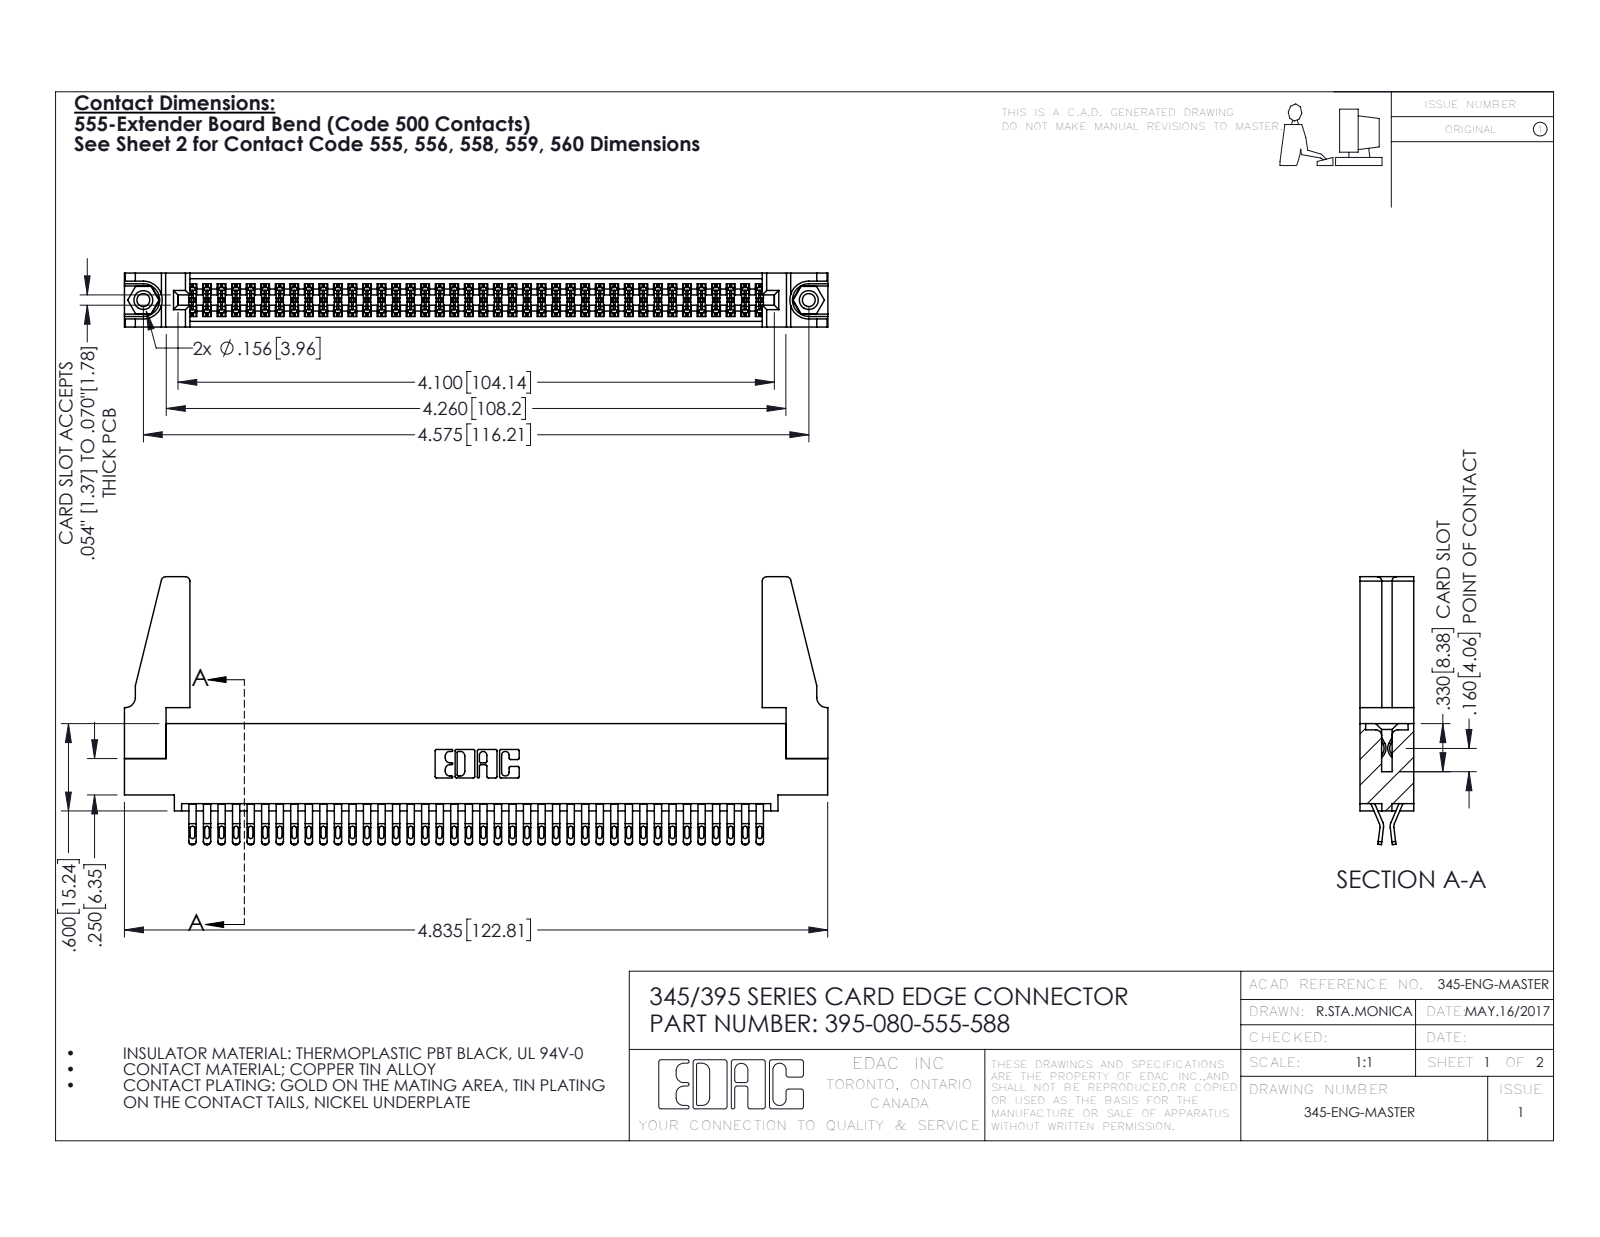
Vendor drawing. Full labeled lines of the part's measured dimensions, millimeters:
Part name (STEP PRODUCT): 345 Part_0.110 Offset - 0.156 Dia-TH; 345-250-001_345-250-001-102; 395-080-555-588; 345-292-001_555 Tail (+1 more)
STEP written by: SolidWorks 2016 (CONFIG_CONTROL_DESIGN)
Units: millimetres
Bodies: 85 solids, 4734 faces (2636 planar, 2082 cylindrical, 16 other)
Overall size (bounding box): 122.8 × 46.8 × 9.4
Volume: 15 300 mm³ · Surface area: 21 830 mm²
Round holes (diameter × count): ⌀2.3 ×2, ⌀3.2 ×2, ⌀4 ×2, ⌀1.6 ×1
Round bosses / shafts (diameter × count): ⌀3.9 ×2
Partial cylindrical surfaces — rounded edges, fillets, slot ends (radius × count): R0.4 ×200, R0.5 ×160, R0.2 ×120, R0.3 ×22, R0.8 ×8, R0.2 ×6, R0.8 ×6, R0.7 ×3
Main face-to-face distances: 1.8, 7.6, 9.4, 0.6, 5.1, 2.5, 6.9, 5.7, 4.4, 3.8
Hole centre spacings: 6.9, 110.2, 116.2
